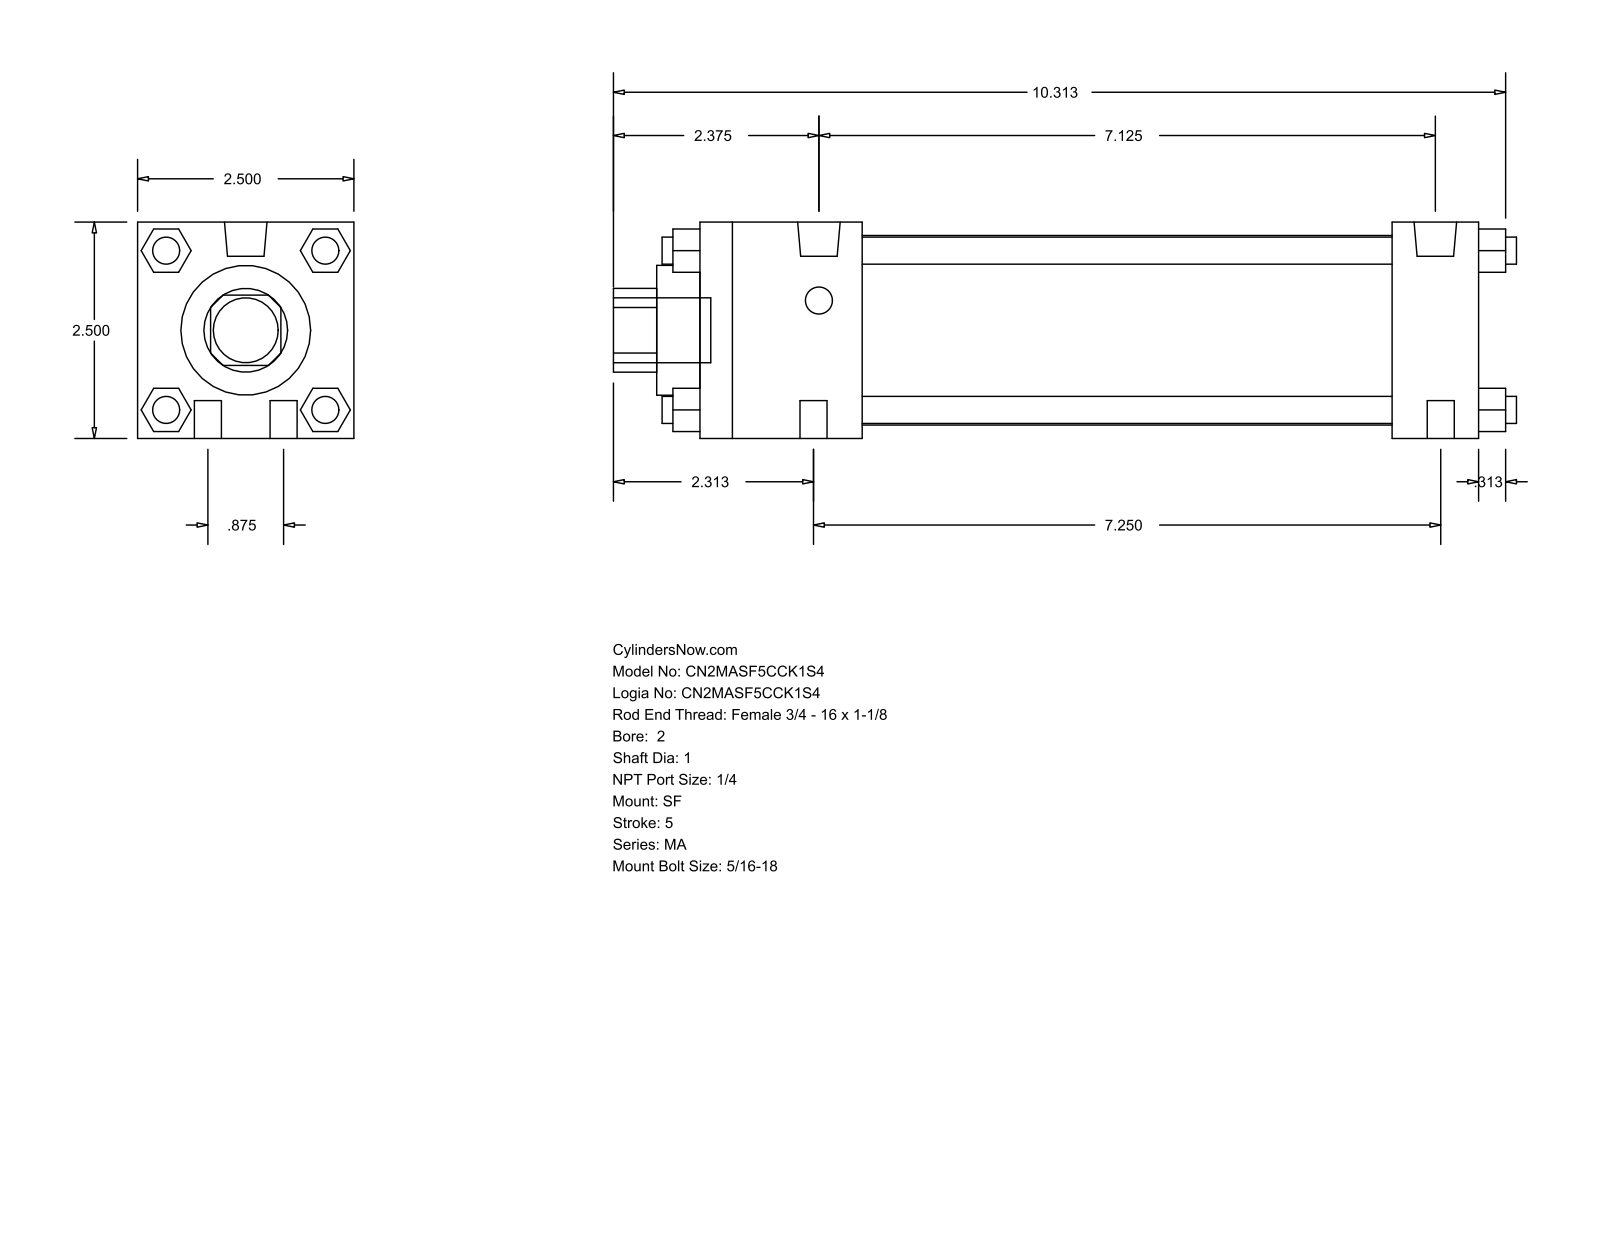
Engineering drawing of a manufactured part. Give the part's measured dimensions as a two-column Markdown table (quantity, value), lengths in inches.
| quantity | value |
| --- | --- |
| part name | MA_SF__0200_1 |
| STEP written by | GSSL Pune (CONFIG_CONTROL_DESIGN) |
| units | inches |
| bodies | 0 solids, 124 faces (94 planar, 30 cylindrical, 0 other) |
| overall size | 10.437 × 2.5 × 2.5 |
| round holes (diameter × count) | 1 × 1, 1.5 × 1, 2.19 × 1 |
| round bosses / shafts (diameter × count) | 0.313 × 10, 0.492 × 2, 0.75 × 1 |
| partial cylindrical surfaces (radius × count) | 0.484 × 1 |
| main face-to-face distances | 2.5, 9, 0.5, 1, 8, 1.875, 6.125, 7.125, 1.593, 0.92 |
